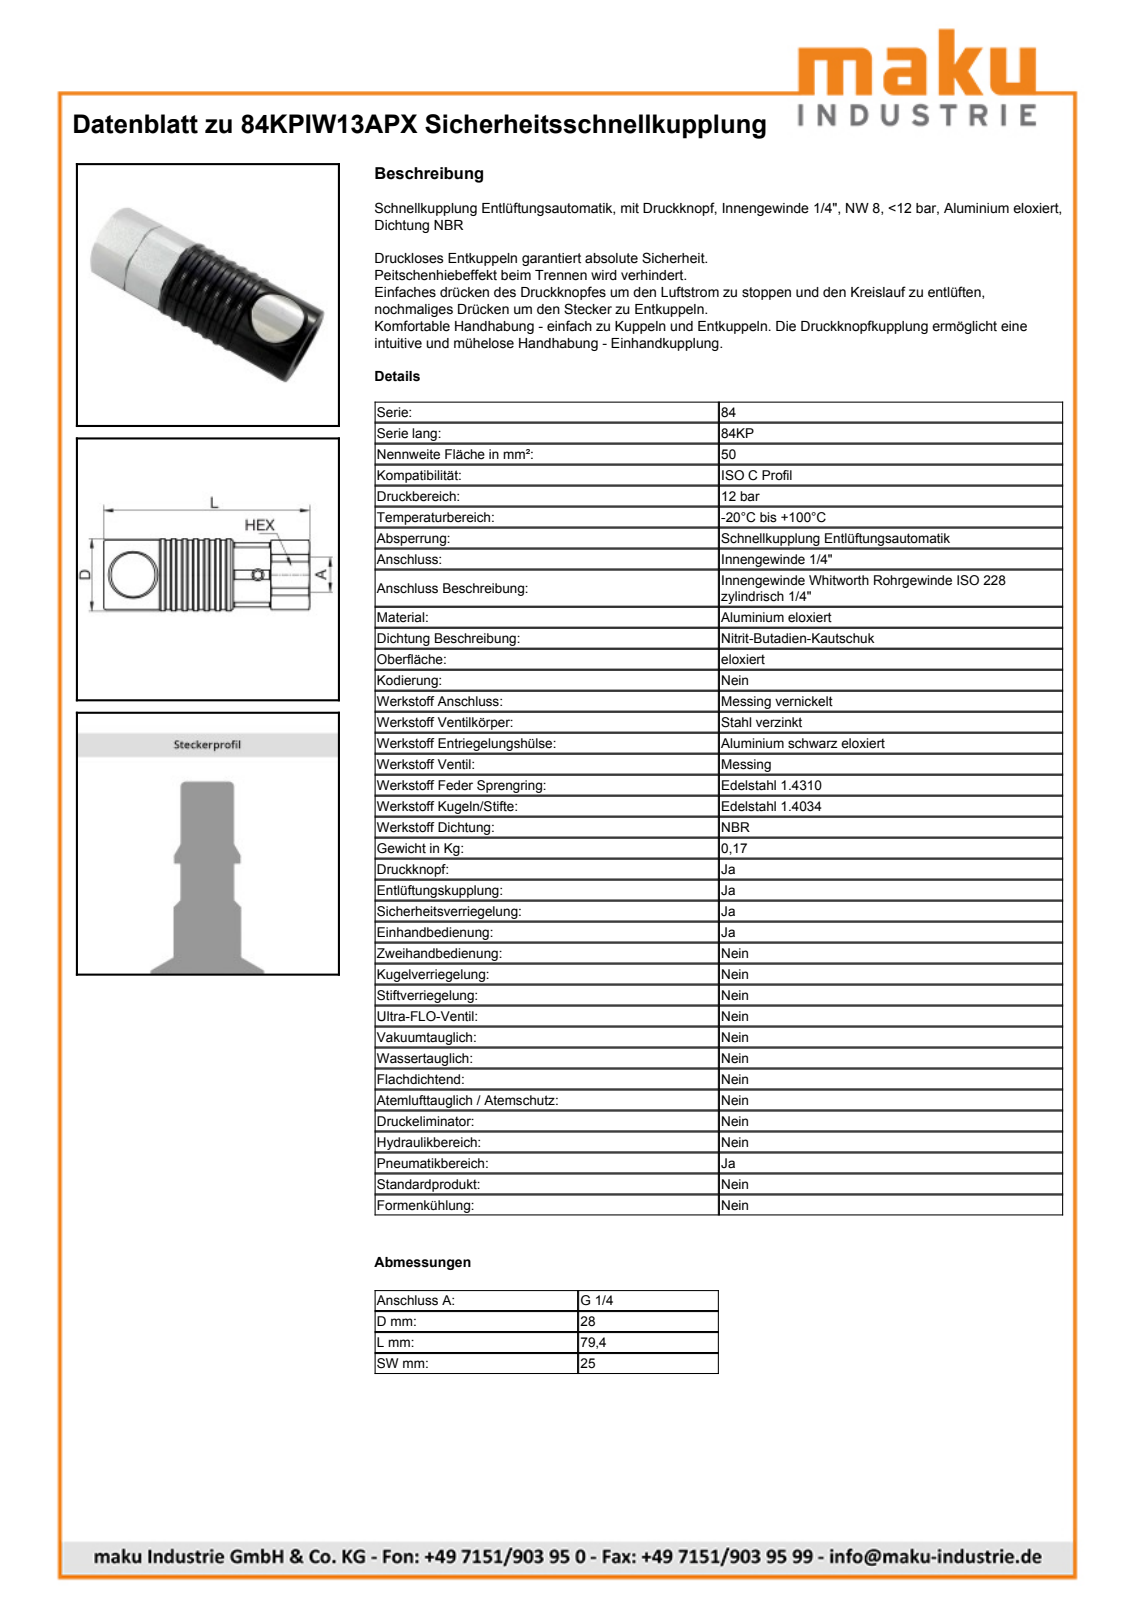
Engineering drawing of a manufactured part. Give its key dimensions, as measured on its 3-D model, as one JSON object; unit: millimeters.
{"part_name": "84KPIW13APX", "step_written_by": "Autodesk Inventor 2019 (CONFIG_CONTROL_DESIGN)", "units": "millimeters", "bodies": {"solids": 33, "faces": 345, "planar": 114, "cylindrical": 123, "other": 108}, "overall_size": [79.4, 28, 28], "volume_mm3": 53672, "surface_area_mm2": 31002, "round_holes": [[3.5, 2], [4, 2], [14, 2], [7.9, 1], [8, 1], [11.2, 1], [11.45, 1], [14.1, 1], [15.5, 1], [16.7, 1], [16.75, 1], [17.1, 1]], "round_bosses_or_shafts": [[28, 1], [27, 1], [25, 1], [23.33, 1], [23.3, 1], [23, 1], [21.42, 1], [19.7, 1]], "partial_cylinders_radius": [[5.53, 1], [8.5, 1], [9.3, 1], [9.75, 1], [13.5, 1], [14.5, 1]], "face_to_face_distances": [25, 64.4, 35.3, 29.1, 24.3, 6.4, 22.7, 41.7, 2.01, 37.31], "hole_center_spacings": [1.2, 1.3, 22, 26.1, 48.1]}
